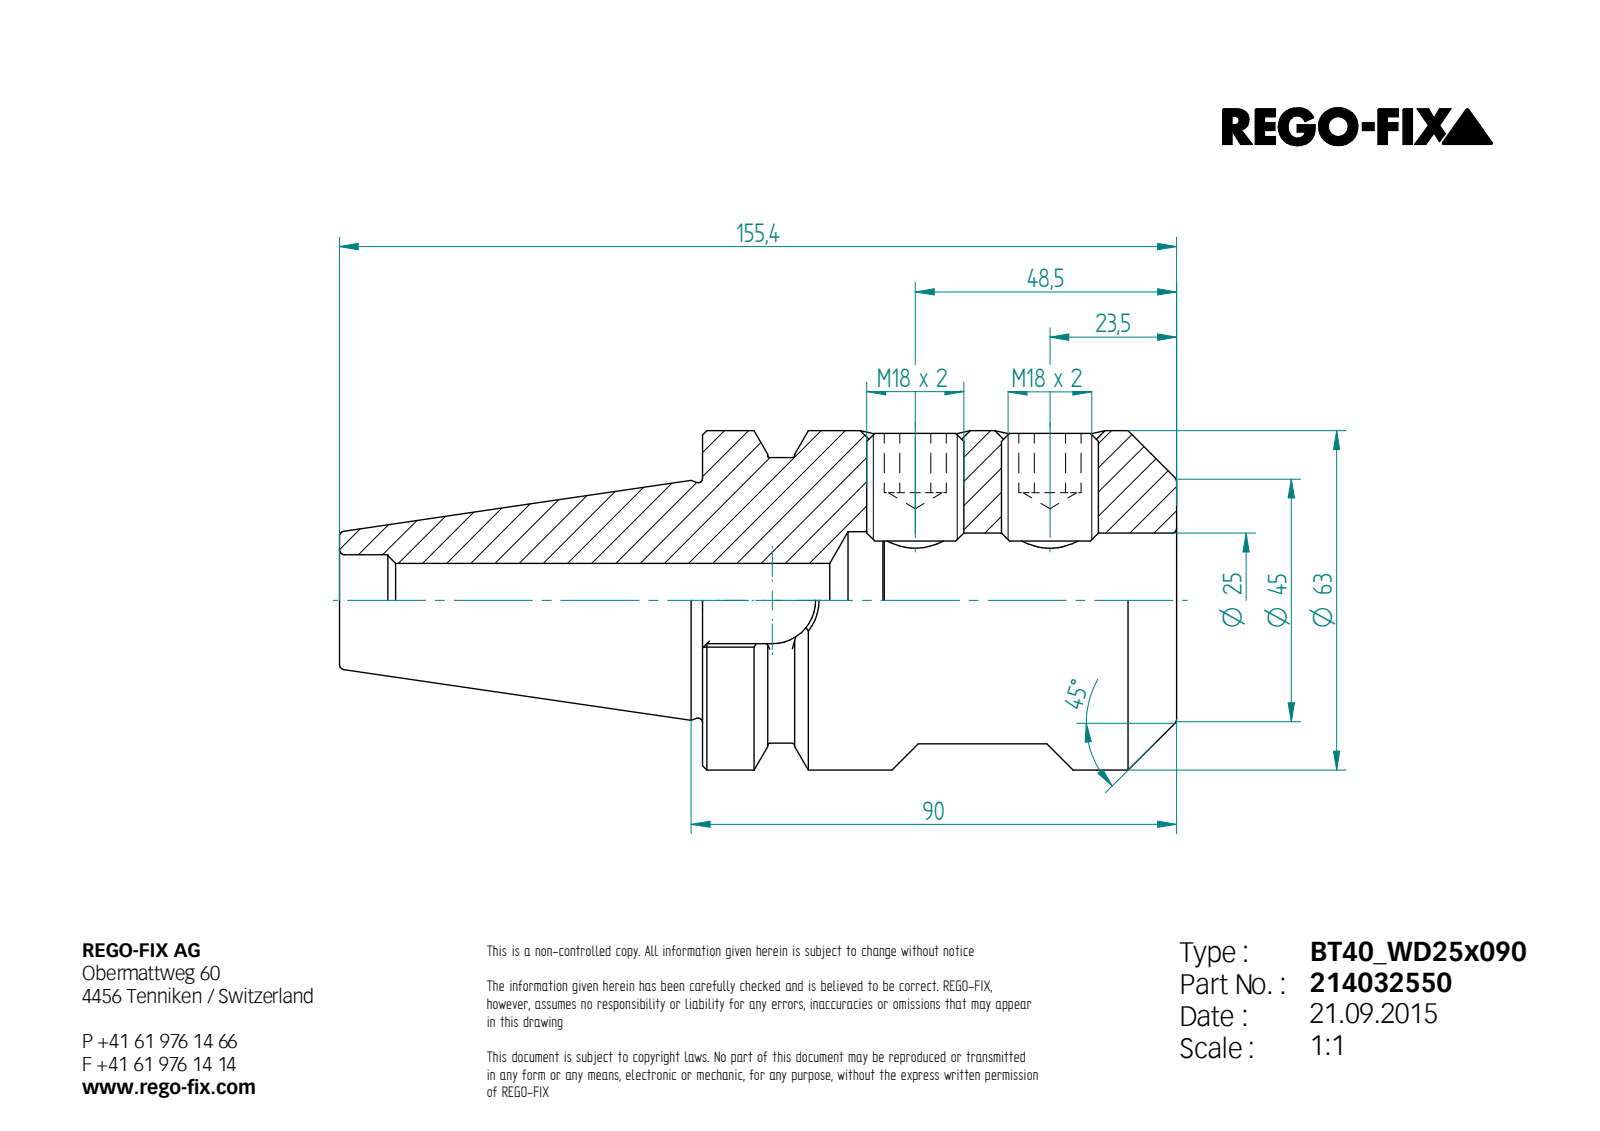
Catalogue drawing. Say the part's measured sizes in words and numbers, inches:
Its 3-D file was written by "Unknown (AUTOMOTIVE_DESIGN)". It is 3 solids with 119 faces: 66 planar, 20 cylindrical and 33 other. Overall it measures 6.118 by 2.48 by 2.48 inches. Its volume is 16.79 cubic inches and its surface area 67.31 square inches. Round holes: 2 of diameter 0.624, 1 of diameter 0.545, 1 of diameter 0.669, 1 of diameter 0.984, 1 of diameter 1.004. Round bosses or shafts: 2 of diameter 0.709, 1 of diameter 2.48, 1 of diameter 2.087. Partial cylindrical surfaces (rounded edges, fillets, slot ends): 4 of radius 0.02, 1 of radius 0.317. The main face-to-face distances are 3.465, 0.394, 1.481, 1.776, 0.852, 0.691, 1.085, 2.269, 0.787, 2.654. The hole center spacings are 0.984.
